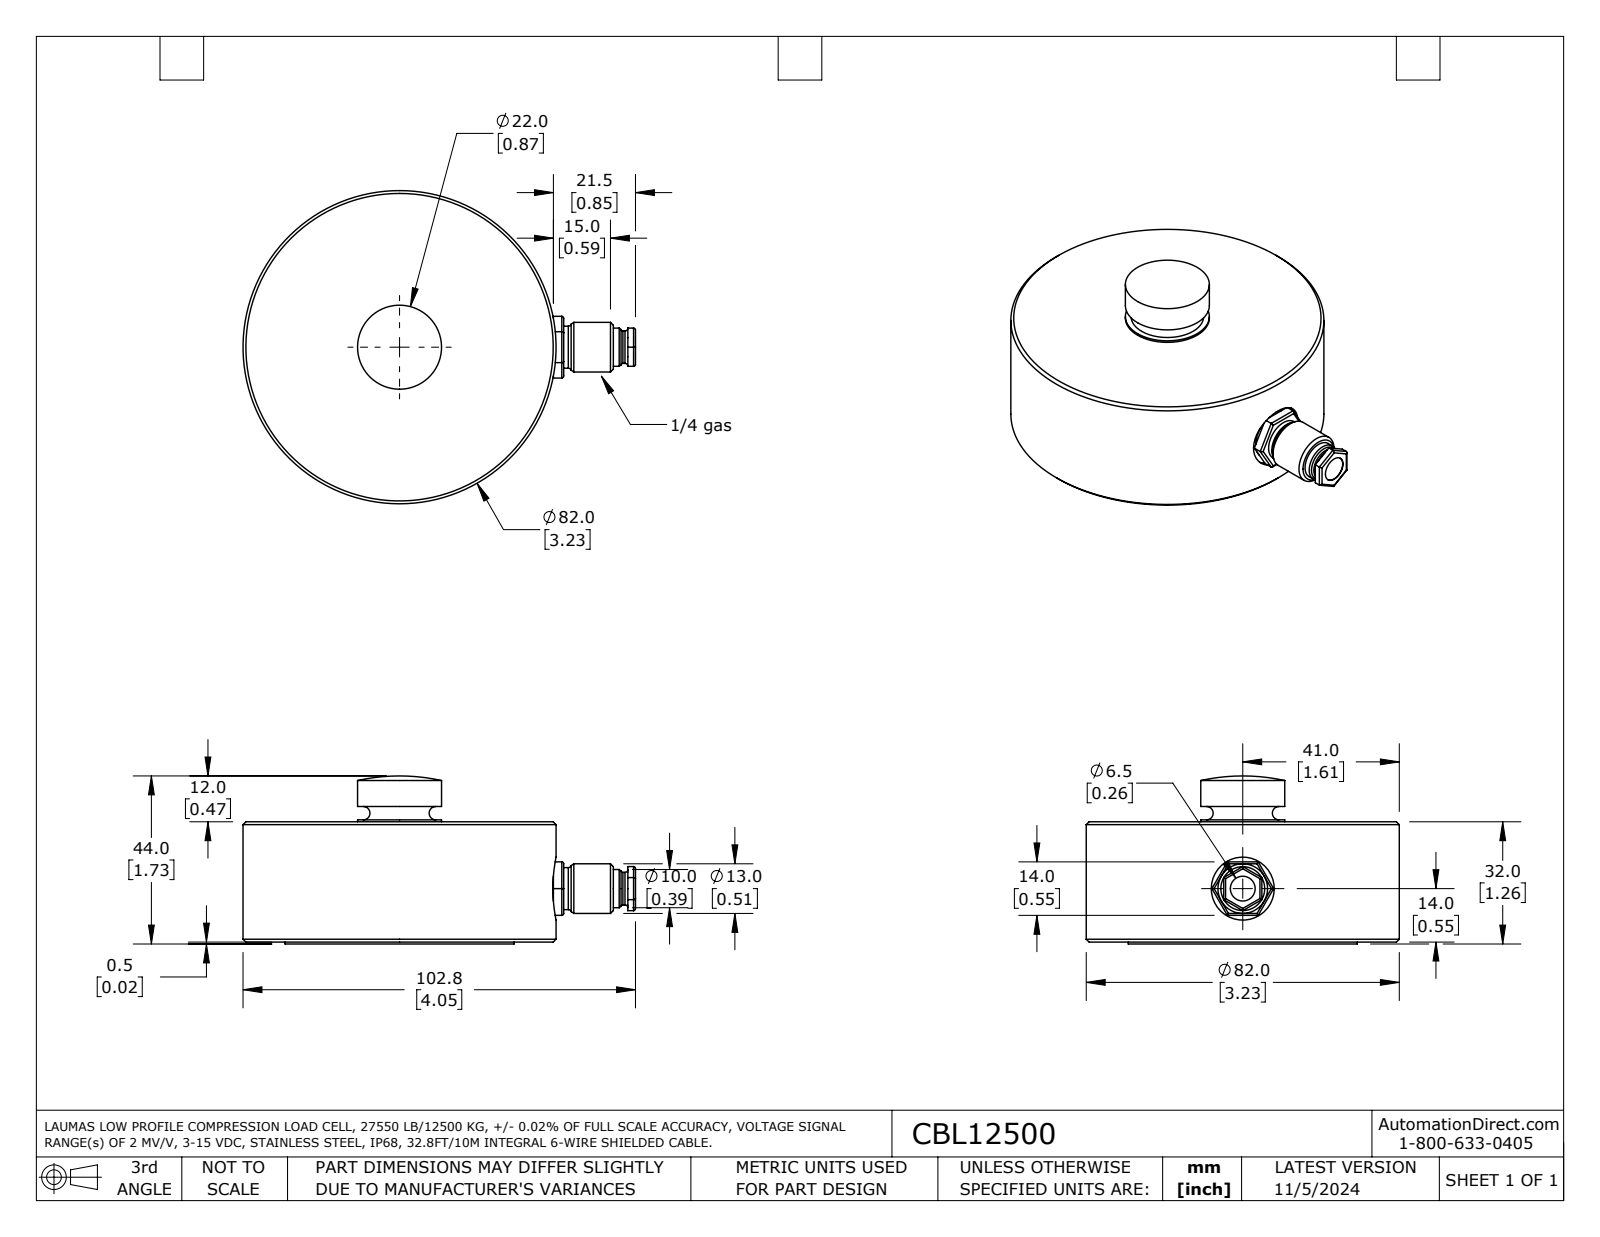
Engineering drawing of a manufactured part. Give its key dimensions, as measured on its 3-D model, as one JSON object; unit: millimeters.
{"part_name": "CBL12500", "step_written_by": "SolidWorks 2021 (AUTOMOTIVE_DESIGN)", "units": "millimeters", "bodies": {"solids": 2, "faces": 86, "planar": 31, "cylindrical": 36, "other": 19}, "overall_size": [102.8, 82, 44], "volume_mm3": 170800, "surface_area_mm2": 21060, "round_holes": [[6.5, 1], [16.5, 1], [54.6, 1]], "round_bosses_or_shafts": [[82, 1], [60, 1], [22, 1], [13.5, 1], [13, 1], [11, 1], [10, 1], [8.5, 1]], "partial_cylinders_radius": [[0.5, 12]], "face_to_face_distances": [30.8, 0.8, 31.5, 0.5, 32, 1.2, 3.5, 32.5, 31.2, 36]}
